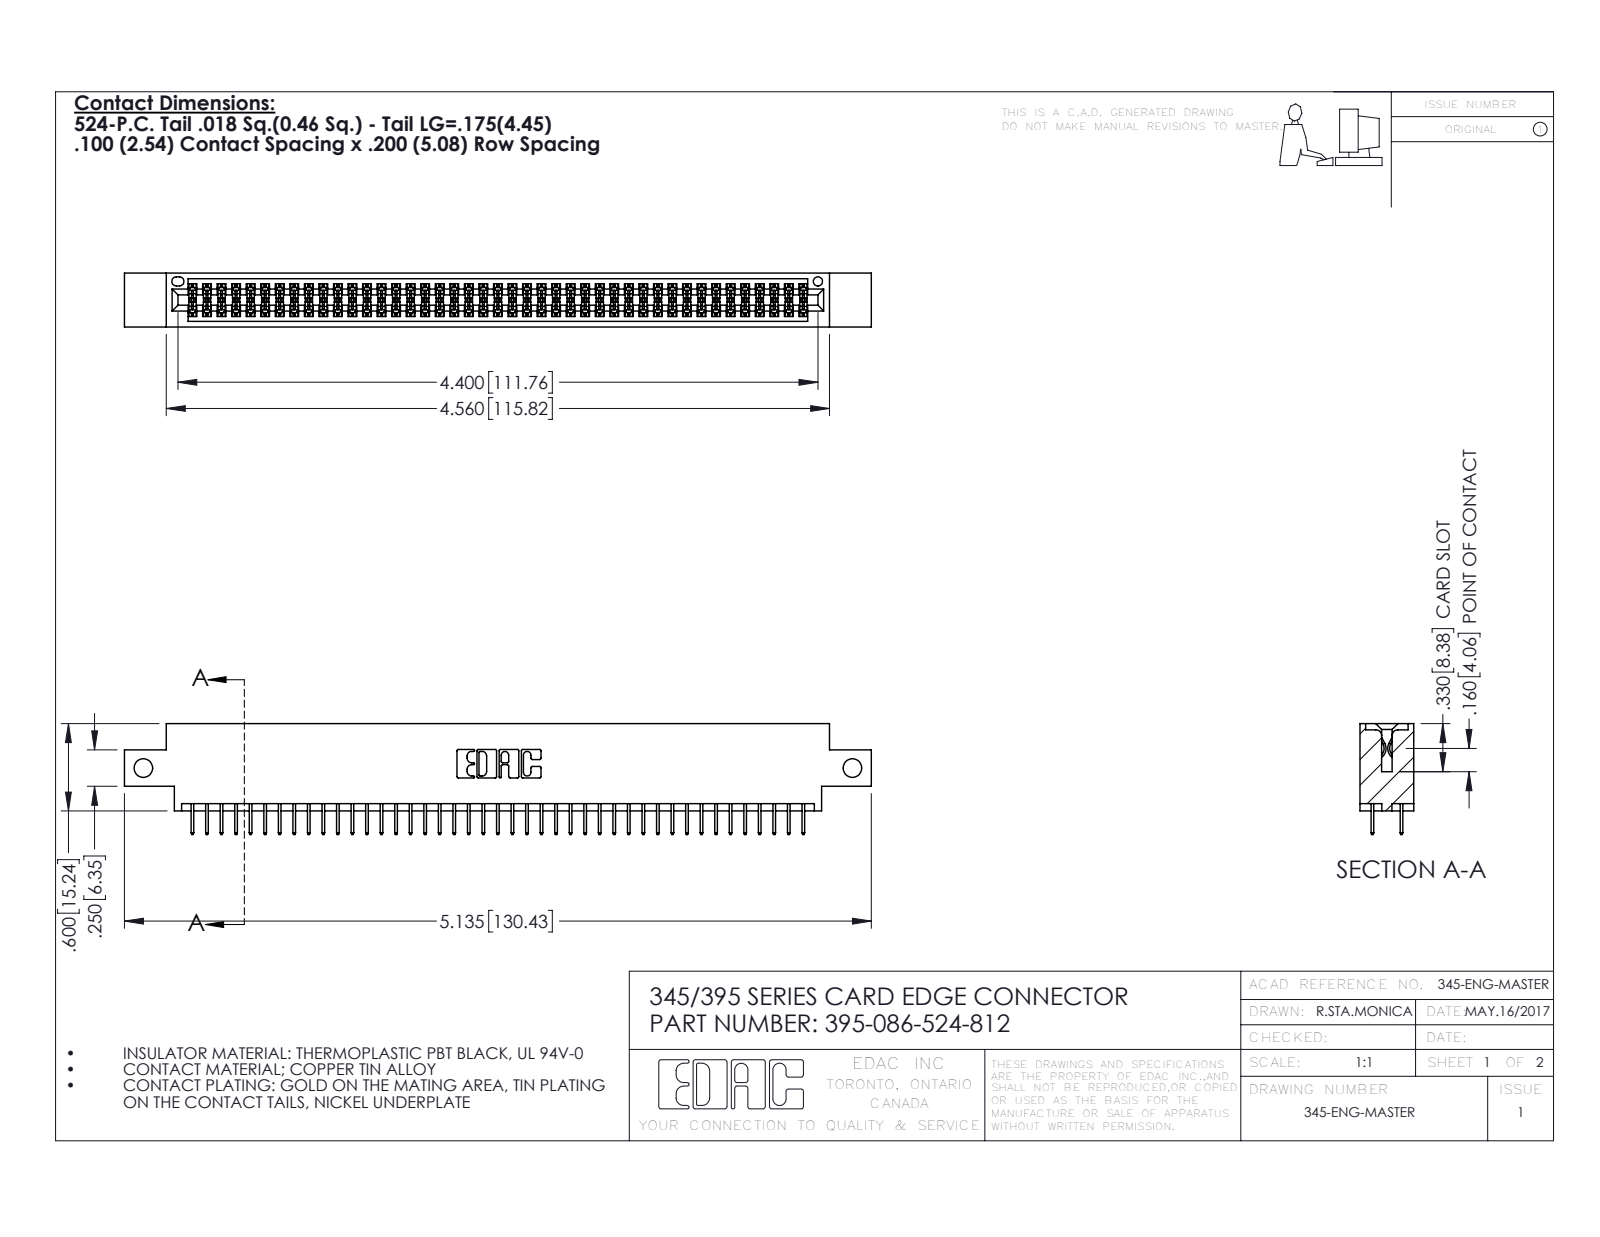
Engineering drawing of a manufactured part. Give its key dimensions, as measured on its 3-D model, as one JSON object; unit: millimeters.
{"part_name": "395-086-524-812; 345-292-001_345-293-124; 345 Part_0.170 Offset - Side Mount", "step_written_by": "SolidWorks 2016 (CONFIG_CONTROL_DESIGN)", "units": "millimeters", "bodies": {"solids": 87, "faces": 4774, "planar": 3438, "cylindrical": 1336, "other": 0}, "overall_size": [130.4, 19.4, 9.4], "volume_mm3": 12400, "surface_area_mm2": 17940, "round_holes": [[3.3, 2], [1.6, 1]], "partial_cylinders_radius": [[0.2, 129], [0.3, 22], [0.2, 6], [0.8, 6], [0.7, 3], [0.4, 2], [0.5, 2], [0.6, 2]], "face_to_face_distances": [1.8, 7.6, 9.4, 5.1, 2.5, 6.9, 0.6, 5.7, 4.4, 1.8], "hole_center_spacings": [123.8]}
